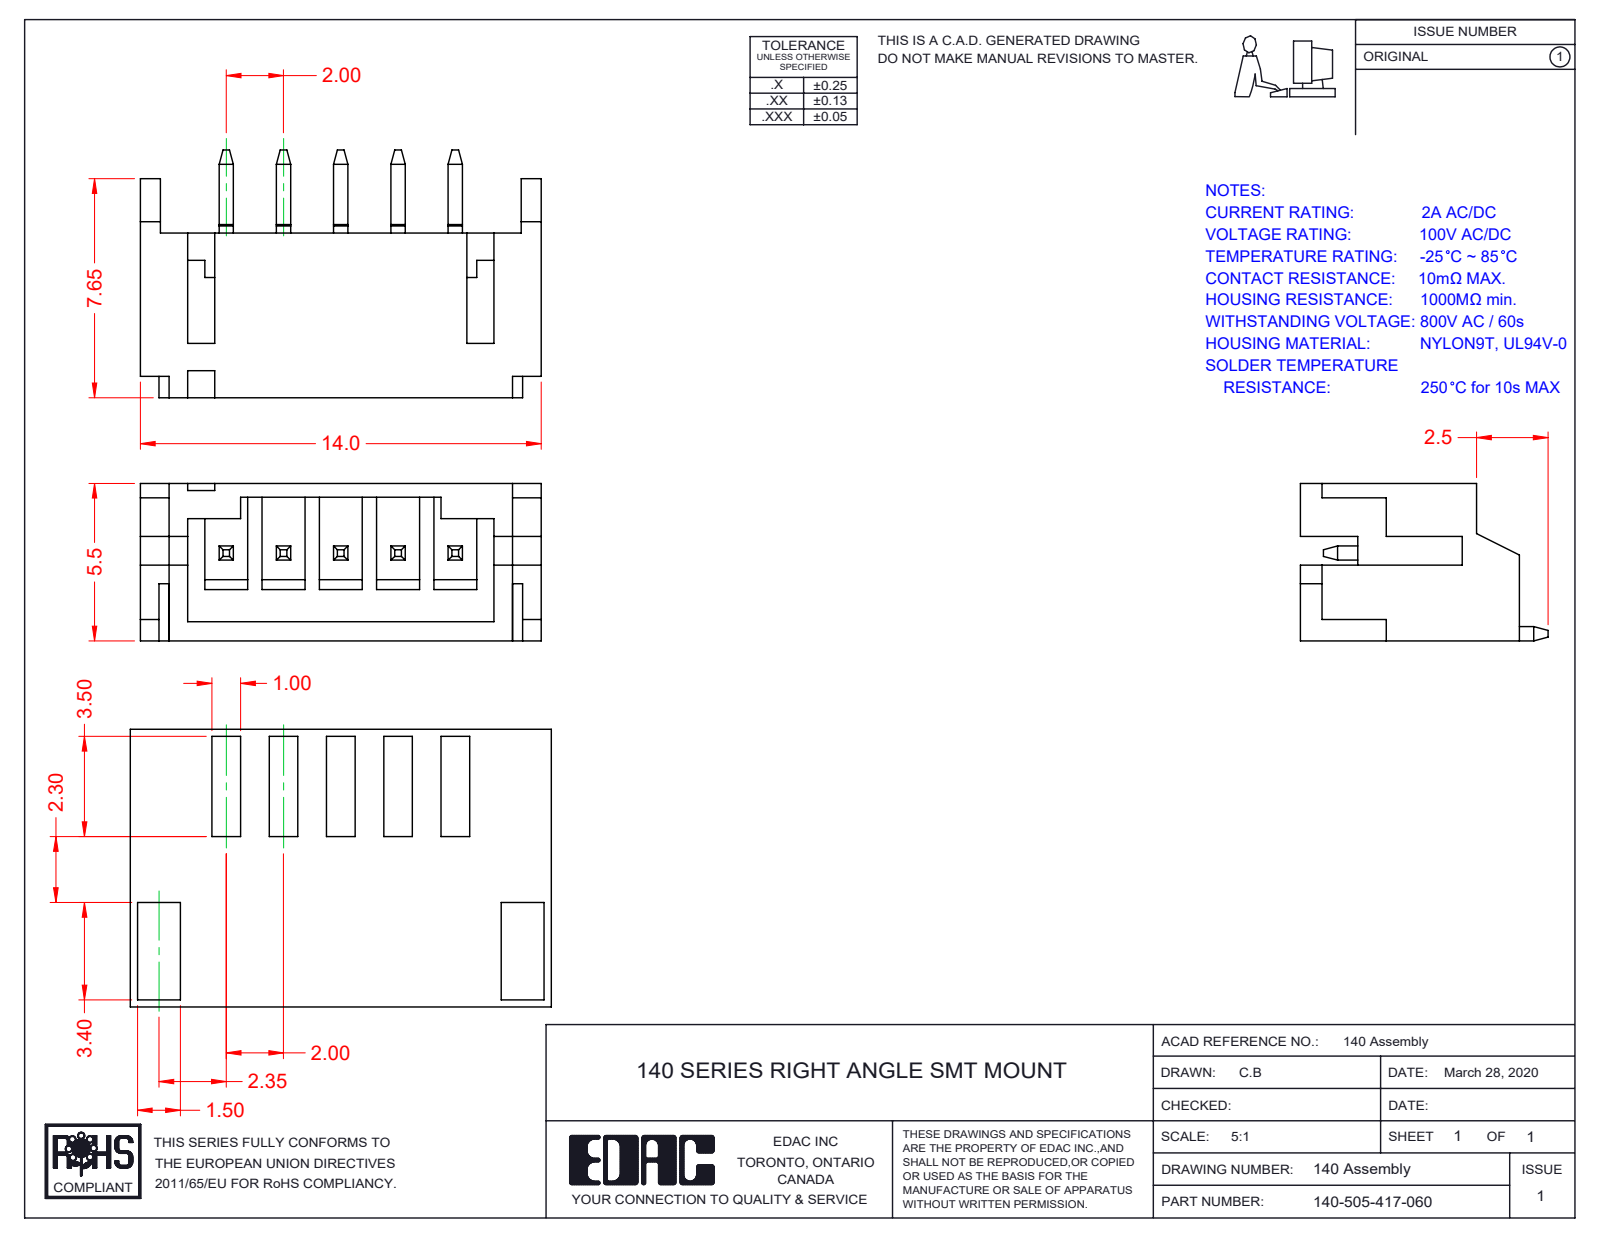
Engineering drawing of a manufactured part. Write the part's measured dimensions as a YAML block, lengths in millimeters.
part_name: "RA SMT Pad; RA SMT Housing_505; RA SMT Contact; 140-505-417-060"
step_written_by: "SolidWorks 2016 (CONFIG_CONTROL_DESIGN)"
units: millimeters
bodies: {solids: 8, faces: 310, planar: 290, cylindrical: 20, other: 0}
overall_size: [14, 8.65, 5.5]
volume: 212
surface_area: 769
partial_cylinders:
  - {radius: 0.55, count: 2}
face_to_face_distances: [0.65, 5.5, 1, 0.67, 0.5, 12.35, 4.83, 0.95, 2, 1.65]
